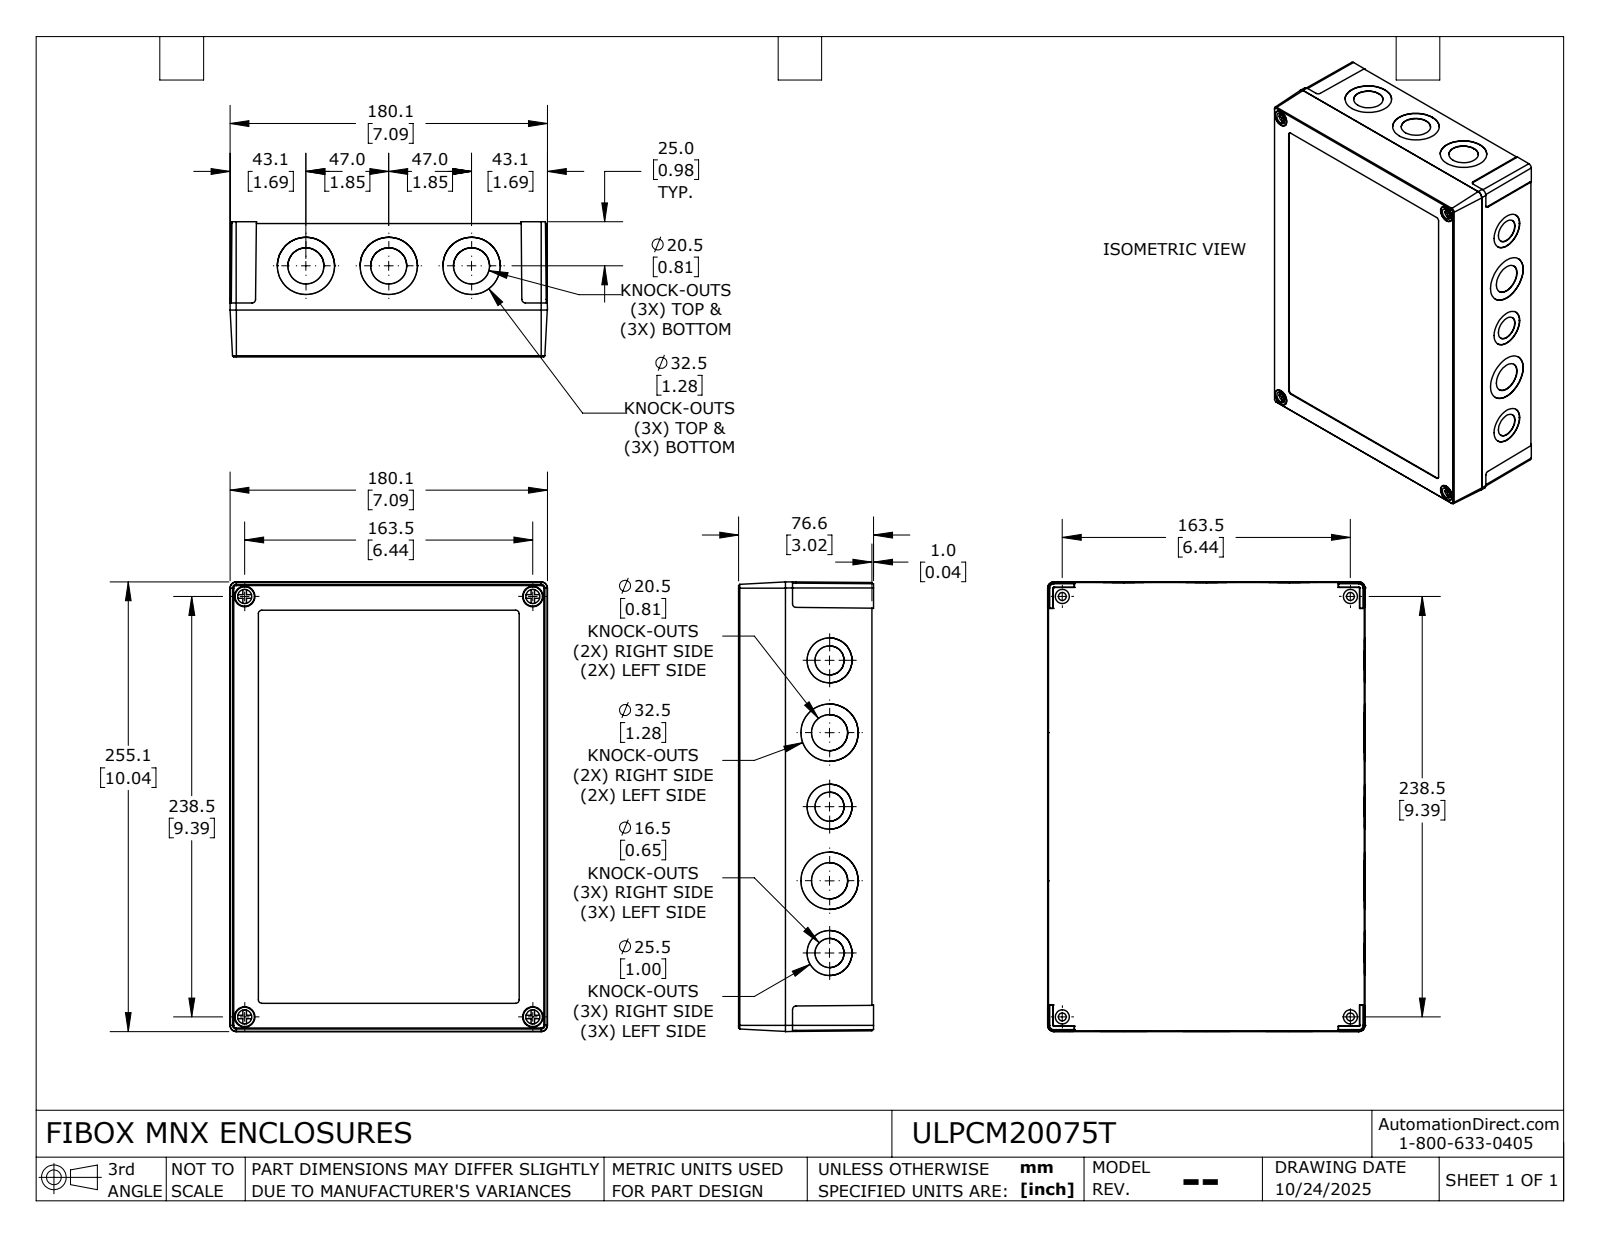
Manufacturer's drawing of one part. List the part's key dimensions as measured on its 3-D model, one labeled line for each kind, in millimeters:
Part name (STEP PRODUCT): ULPCM20075T_Default
STEP written by: SolidWorks 2024 (CONFIG_CONTROL_DESIGN)
Units: millimetres
Bodies: 6 solids, 678 faces (350 planar, 272 cylindrical, 56 other)
Overall size (bounding box): 255.1 × 180.1 × 76.6
Volume: 495 500 mm³ · Surface area: 323 900 mm²
Round holes (diameter × count): ⌀3.2 ×20, ⌀4 ×20, ⌀20.5 ×10, ⌀32.5 ×10, ⌀16.5 ×6, ⌀25.5 ×6, ⌀4.5 ×4, ⌀8 ×4, ⌀11.6 ×4
Round bosses / shafts (diameter × count): ⌀8 ×16, ⌀11 ×4, ⌀7.2 ×4, ⌀7 ×4
Partial cylindrical surfaces — rounded edges, fillets, slot ends (radius × count): R2 ×8, R2.8 ×6, R1.1 ×4, R5 ×4, R1.2 ×2
Main face-to-face distances: 72.9, 3, 69.9, 2.2, 75.1, 72.1, 4.2, 72.6, 0.5, 2.7
Hole centre spacings: 125, 49.3, 128.2, 20.6, 22.1, 26.6, 33.9, 38.3
